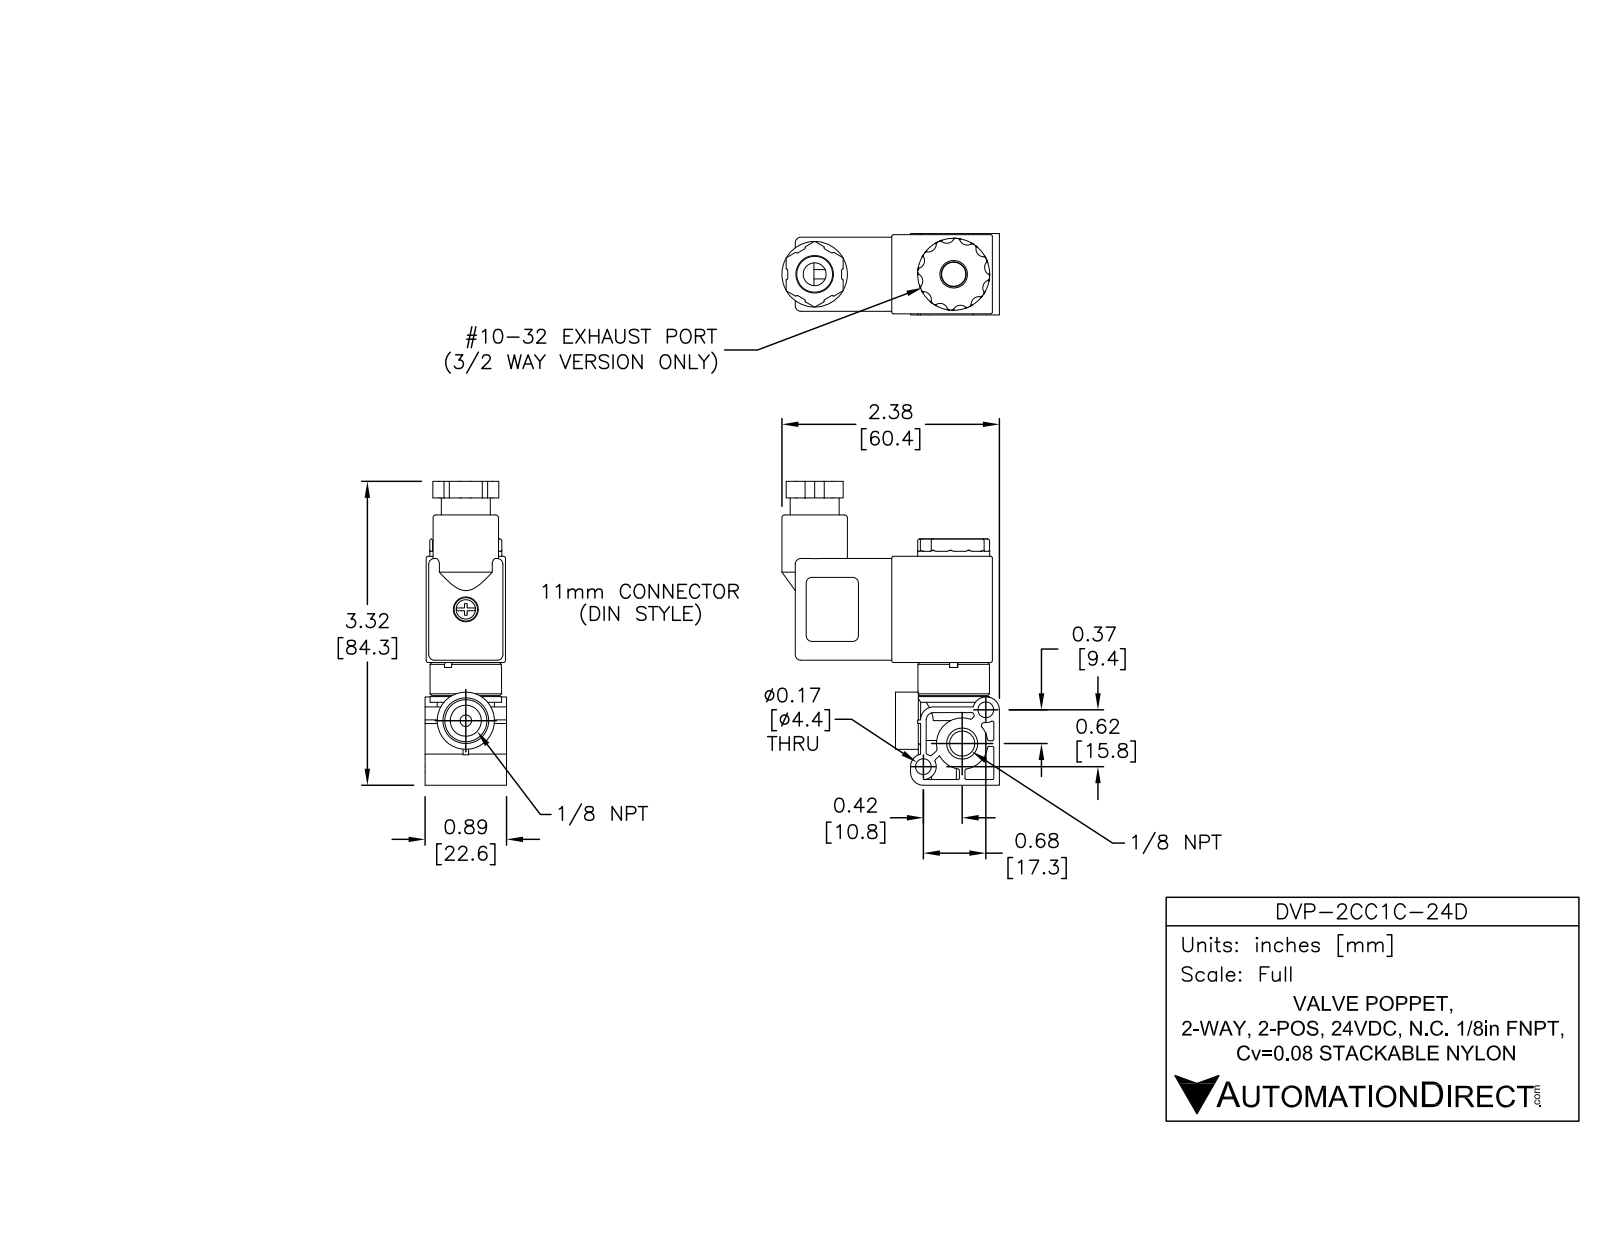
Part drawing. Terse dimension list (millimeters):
name: DVP-2CC1C-24D
written by: SolidWorks 2015 (AUTOMOTIVE_DESIGN)
unit: mm
bodies: 2 solids, 1445 faces (660 planar, 308 cylindrical, 477 other)
size: 84.3 × 60.4 × 22.6
volume: 35 000 mm³; area: 25 260 mm²
holes: 2× ⌀2.5, 2× ⌀3.2, 2× ⌀3.8, 2× ⌀4.4, 2× ⌀8.6, 1× ⌀2.6, 1× ⌀4.2, 1× ⌀6.4, 1× ⌀6.8, 1× ⌀6.9, 1× ⌀7, 1× ⌀8.2
bosses: 2× ⌀15.9, 1× ⌀20, 1× ⌀19.8, 1× ⌀18.2, 1× ⌀13.7, 1× ⌀13.6, 1× ⌀13.3, 1× ⌀12.7
rounds: 28× R0.4, 25× R0.3, 24× R0.6, 12× R0.5, 12× R1.6, 12× R2.2, 5× R0.8, 4× R3.6
face distances: 2, 20, 1.3, 20.3, 19.3, 0.7, 21.3, 22, 28.9, 18
hole spacings: 8.3, 10.7, 11.4, 12.5, 13.3, 18.6, 23.4, 24
